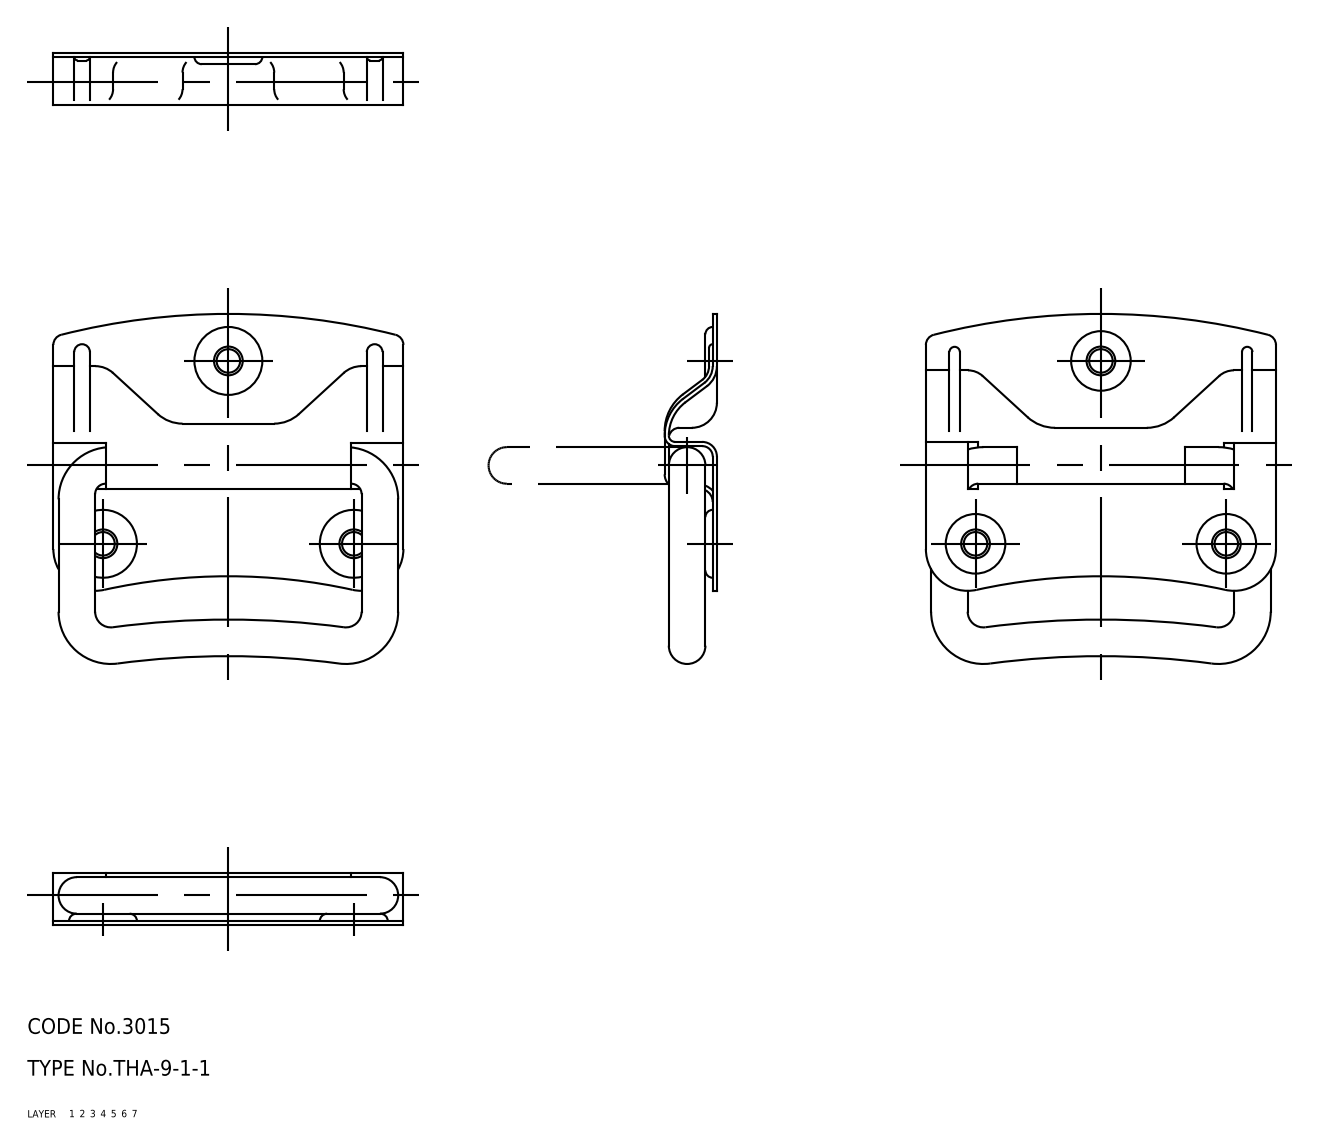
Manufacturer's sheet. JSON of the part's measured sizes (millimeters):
{"part_name": "grip; base; THA_9_1_1_23619_36", "step_written_by": "CADfix (AUTOMOTIVE_DESIGN)", "units": "millimeters", "bodies": {"solids": 2, "faces": 259, "planar": 0, "cylindrical": 0, "other": 259}, "overall_size": [67, 67, 10], "volume_mm3": 8848, "surface_area_mm2": 11846}
